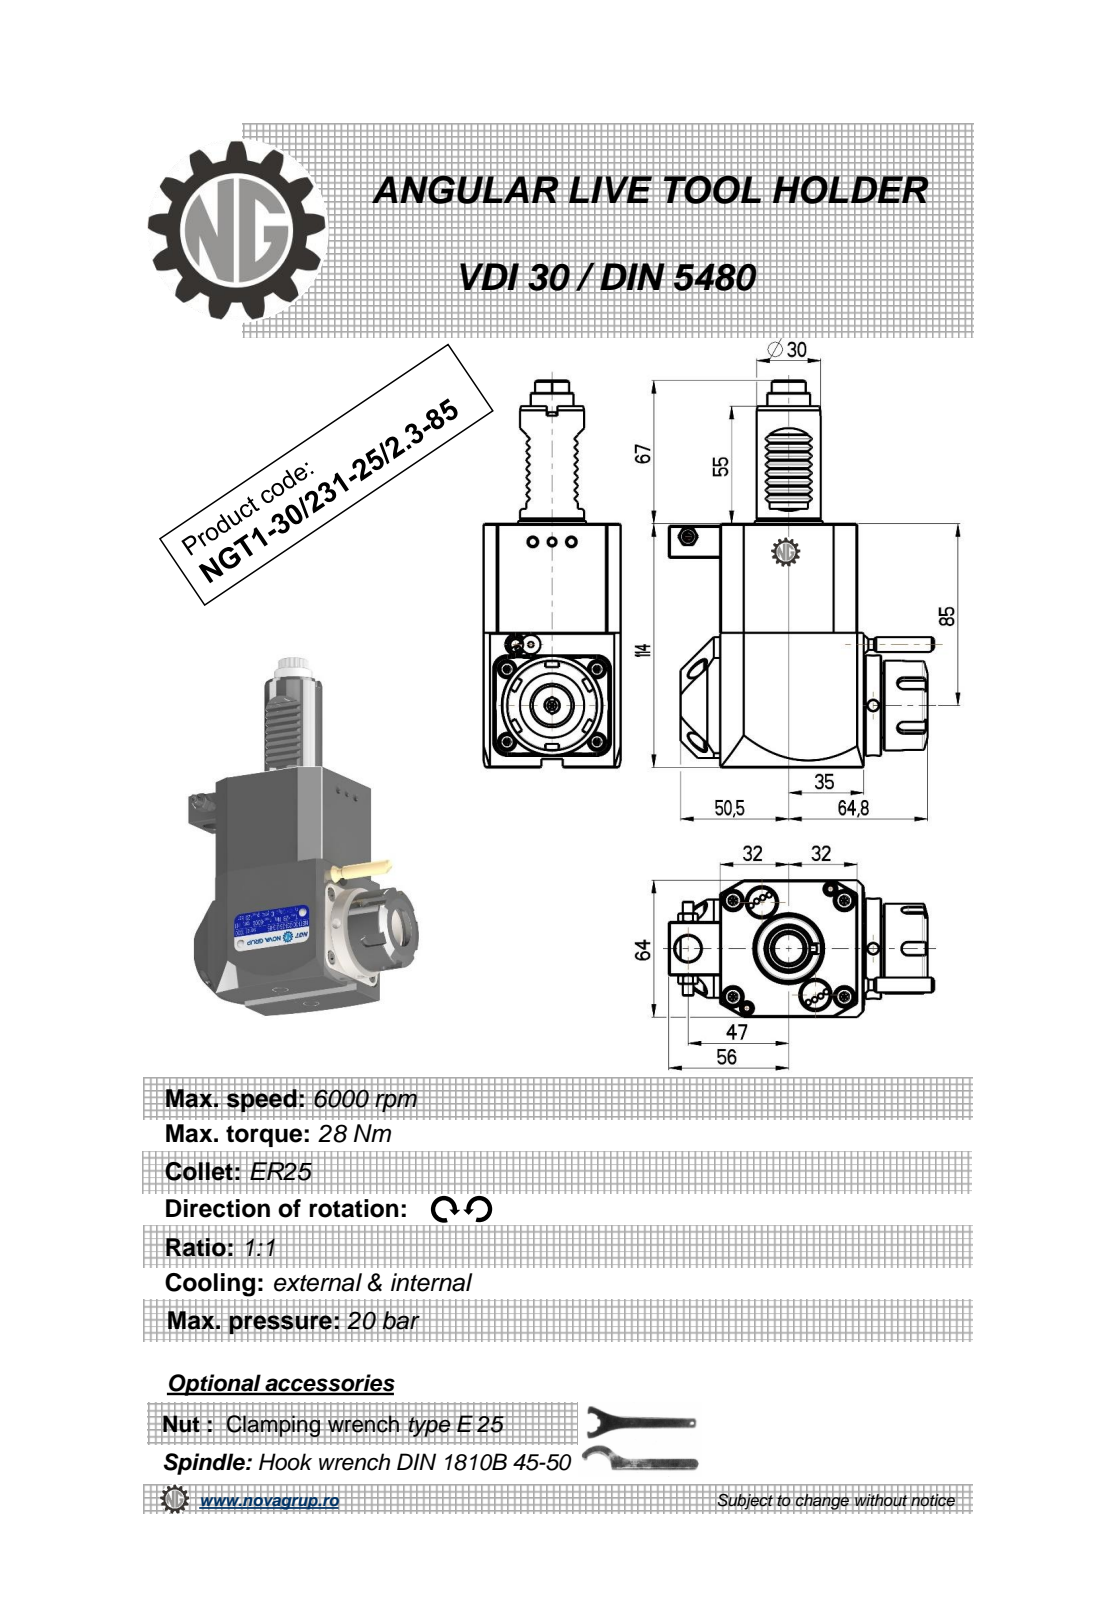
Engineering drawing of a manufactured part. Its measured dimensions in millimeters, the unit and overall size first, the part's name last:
Units: millimetres
Overall size (bounding box): 181 × 123.83 × 64
Round holes (diameter × count): ⌀5 ×2, ⌀2.5 ×1, ⌀3 ×1, ⌀4.2 ×1, ⌀9.5 ×1, ⌀12 ×1, ⌀20.3 ×1
Round bosses / shafts (diameter × count): ⌀8.96 ×2, ⌀5 ×2, ⌀47 ×1, ⌀42 ×1, ⌀35 ×1, ⌀30 ×1, ⌀20 ×1, ⌀7 ×1
Partial cylindrical surfaces — rounded edges, fillets, slot ends (radius × count): R1.98 ×36, R0.3 ×16, R0.26 ×12, R3 ×5, R160 ×2, R7.08 ×1, R7.92 ×1, R13 ×1
Main face-to-face distances: 64, 114, 0.5, 67, 67.2, 3.2, 76.42, 7.5, 3, 2.83
Hole centre spacings: 33.19, 50.92, 76.5, 86.45, 117.11
Volume: 582 344 mm³ · Surface area: 55 713 mm²
Bodies: 1 solid, 550 faces (223 planar, 161 cylindrical, 166 other)
Part name (STEP PRODUCT): NGT1_30_231_25_2_3_85
STEP written by: PRO/ENGINEER BY PARAMETRIC TECHNOLOGY CORPORATION, 2010280 (CONFIG_CONTROL_DESIGN)
